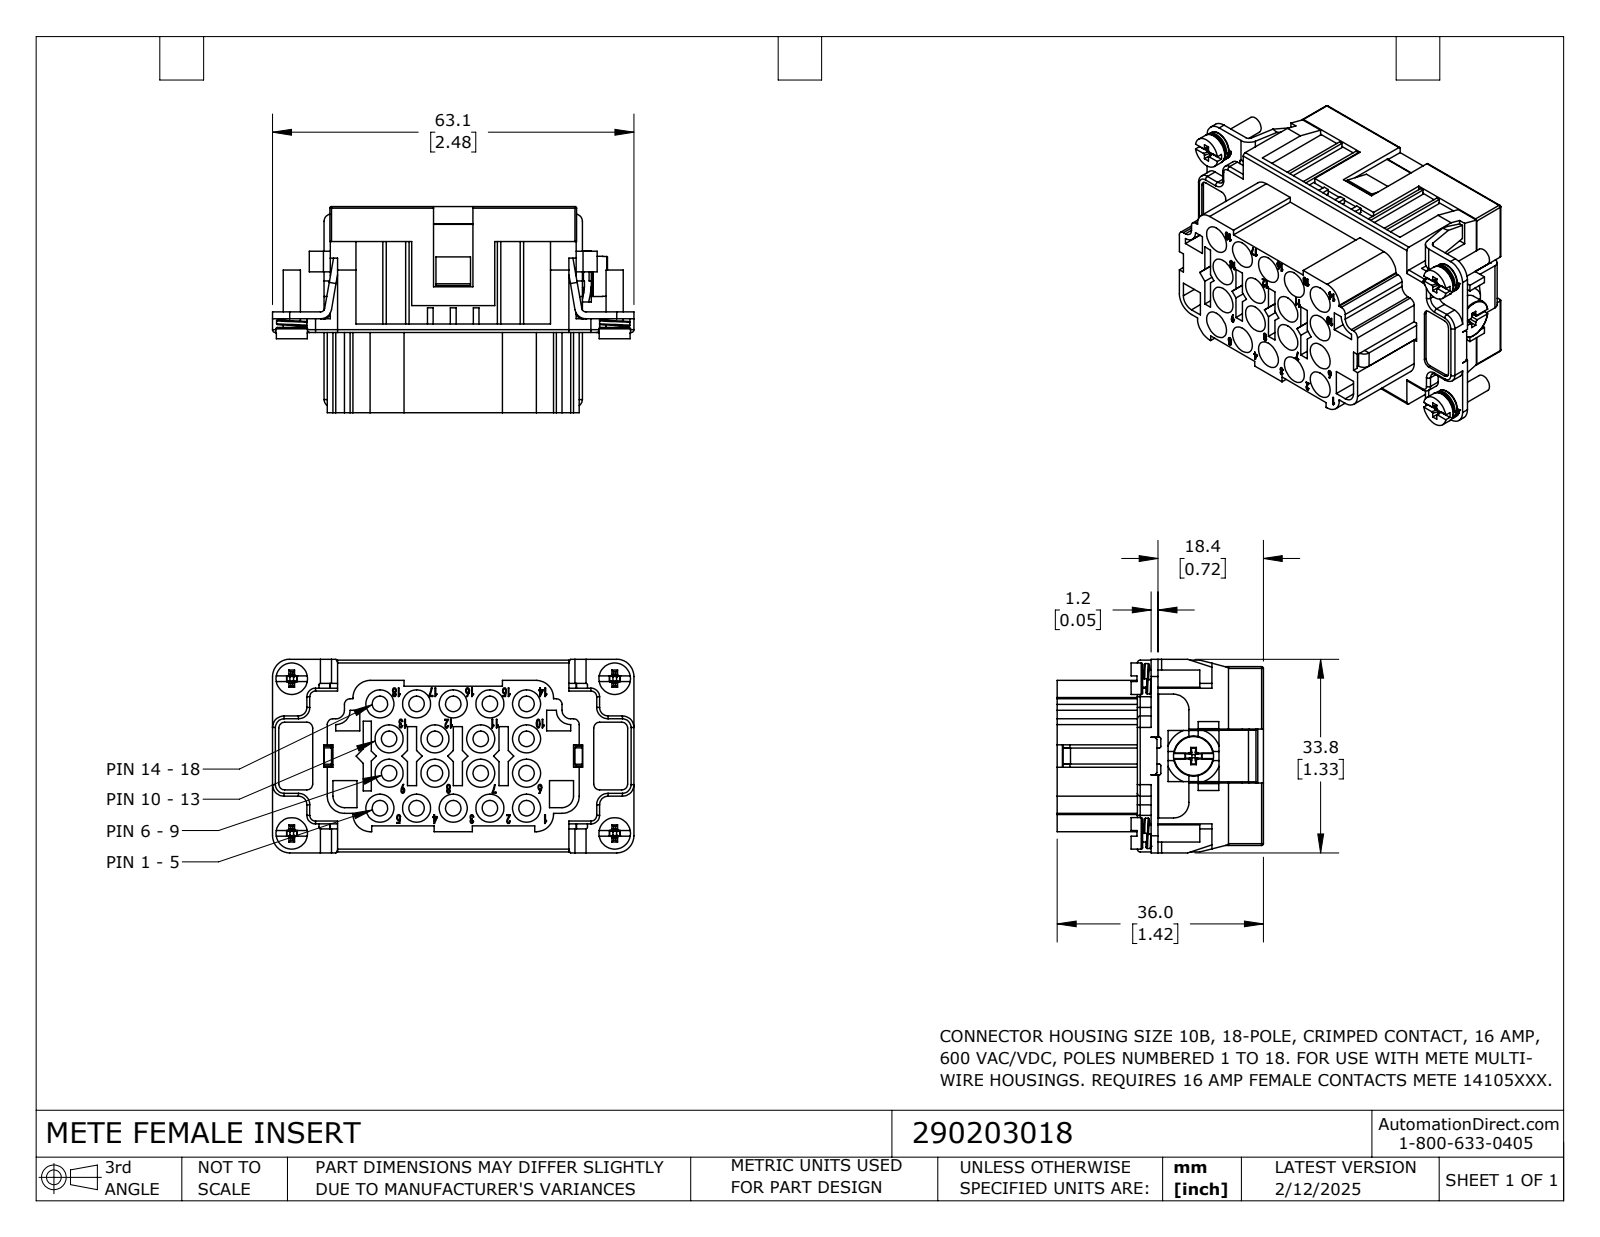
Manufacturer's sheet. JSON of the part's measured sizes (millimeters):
{"part_name": "290203018", "step_written_by": "SolidWorks 2024 (CONFIG_CONTROL_DESIGN)", "units": "millimeters", "bodies": {"solids": 1, "faces": 2030, "planar": 1166, "cylindrical": 521, "other": 343}, "overall_size": [63.1, 36, 33.8], "volume_mm3": 28978, "surface_area_mm2": 31912, "round_holes": [[2.7, 18], [4.8, 18], [4.9, 18], [1.7, 8], [2.8, 3], [3.3, 1]], "round_bosses_or_shafts": [[1.6, 8], [5.5, 4], [5.3, 4], [3, 4], [2.7, 3], [7, 1], [5.1, 1], [3.9, 1]], "partial_cylinders_radius": [[0.25, 32], [1.5, 28], [3, 28], [0.3, 20], [0.5, 18], [4.2, 18], [1, 12], [0.1, 10]], "face_to_face_distances": [1.2, 2.4, 1, 27.8, 14, 30, 28.8, 26.6, 3, 4.55], "hole_center_spacings": [16.17, 3.97, 6.4, 8, 19.29, 22.52, 18.2, 4.31]}
